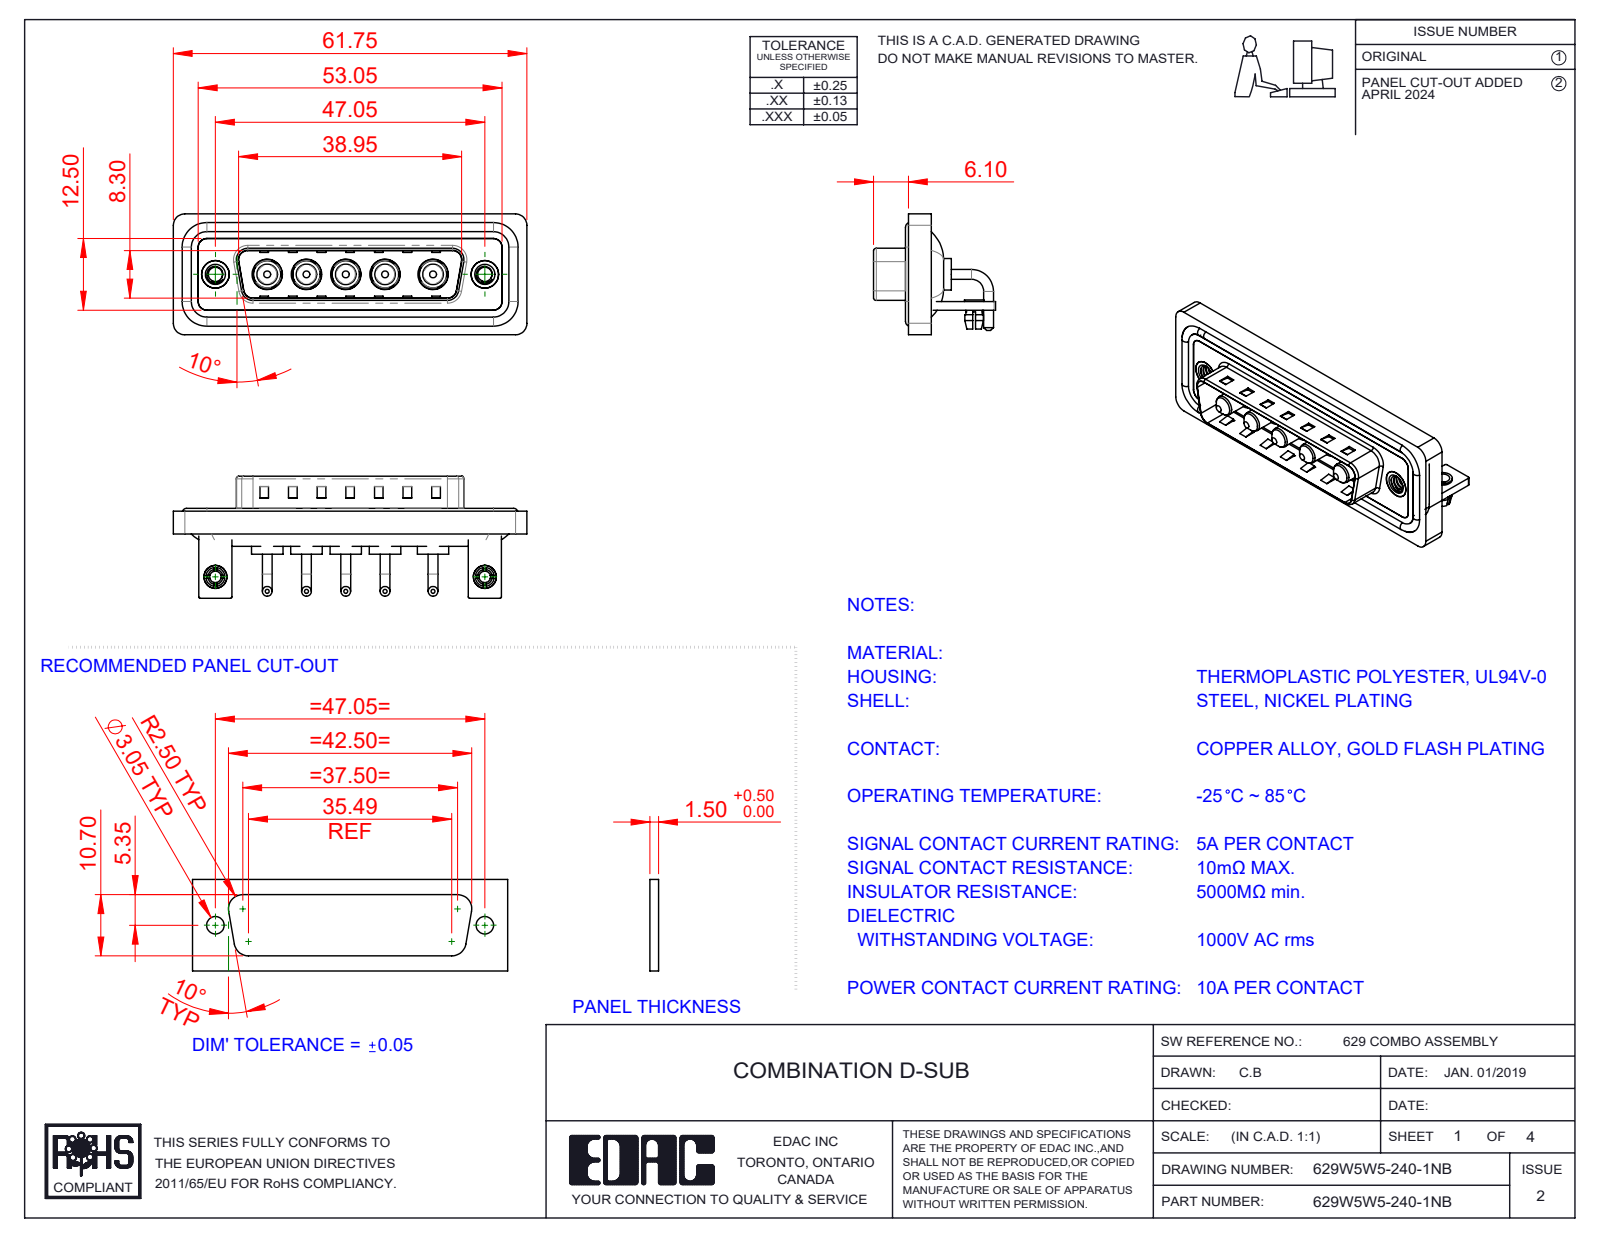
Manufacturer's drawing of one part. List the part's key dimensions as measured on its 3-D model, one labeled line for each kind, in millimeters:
Part name (STEP PRODUCT): 629Combo Housing_5W5; 629Combo Shell Rear_25 Contacts; Power Pin_10A RA; 629Combo Stabilizer Bracket (+5 more)
STEP written by: SolidWorks 2023 (CONFIG_CONTROL_DESIGN)
Units: millimetres
Bodies: 21 solids, 828 faces (327 planar, 343 cylindrical, 158 other)
Overall size (bounding box): 61.75 × 21.3 × 21.1
Volume: 7 820 mm³ · Surface area: 12 816 mm²
Round holes (diameter × count): ⌀4.85 ×5, ⌀5.3 ×5, ⌀2.5 ×4, ⌀2 ×2, ⌀3.2 ×2, ⌀4 ×2, ⌀4.8 ×2, ⌀5 ×2
Round bosses / shafts (diameter × count): ⌀1.7 ×10, ⌀5.5 ×5, ⌀5.2 ×5, ⌀4.75 ×5, ⌀3.75 ×5, ⌀3.6 ×5, ⌀1.6 ×4, ⌀4.9 ×2
Partial cylindrical surfaces — rounded edges, fillets, slot ends (radius × count): R2 ×19, R1.5 ×18, R0.25 ×16, R0.5 ×9, R1.6 ×8, R2.1 ×5, R0.6 ×4, R0.65 ×4
Main face-to-face distances: 0.4, 1.5, 2.9, 0.8, 2.1, 3.7, 1.1, 4.5, 4.1, 1.2
Hole centre spacings: 6.86, 13.73, 47.05, 6.85, 6.87, 8.37, 8.38, 9.04
